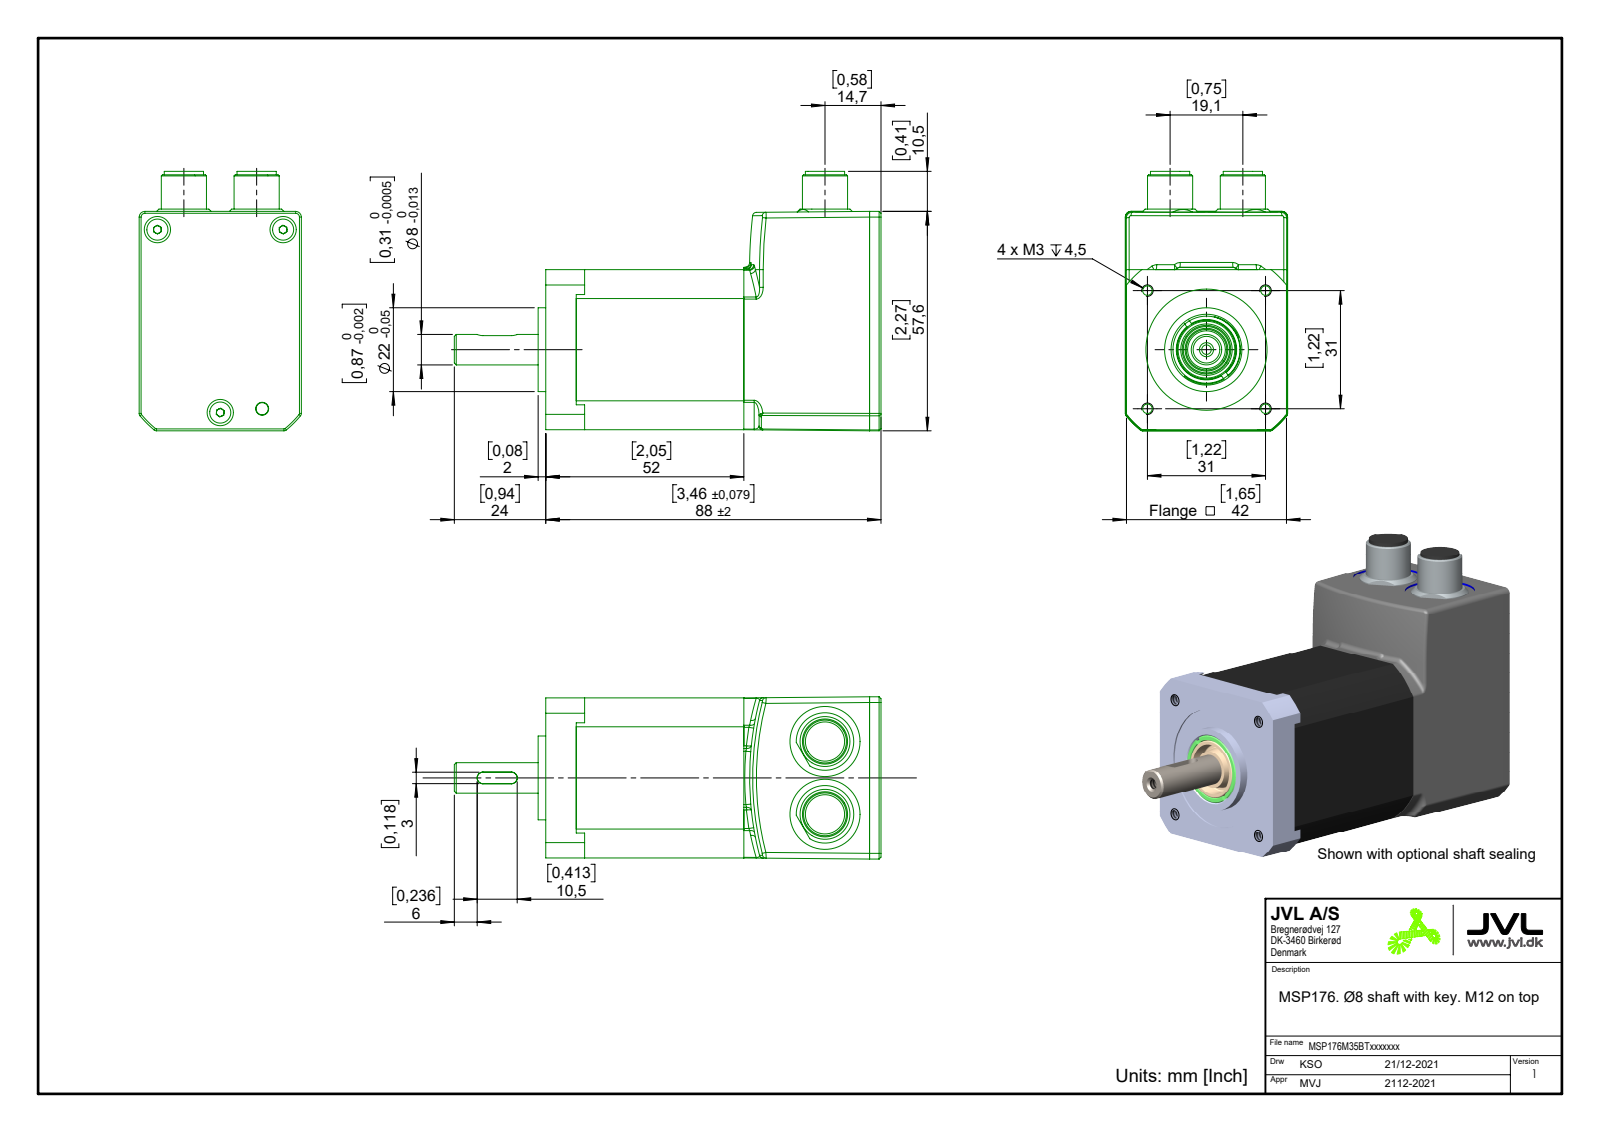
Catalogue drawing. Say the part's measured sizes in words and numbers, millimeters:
The part is named "MSP176M35BTxxxxxxx". Its 3-D file was written by "FreeCAD (AUTOMOTIVE_DESIGN)". It is 5 solids with 335 faces: 136 planar, 73 cylindrical and 126 other. Overall it measures 112 by 68.08 by 42.58 millimeters. Its volume is 175 501 cubic millimeters and its surface area 23 226 square millimeters. Round holes: 5 of diameter 2.5, 3 of diameter 3.3, 2 of diameter 18.4, 1 of diameter 2.8, 1 of diameter 3.4, 1 of diameter 9, 1 of diameter 31.8. Round bosses or shafts: 3 of diameter 5.54, 3 of diameter 3, 2 of diameter 15.1, 2 of diameter 11.85, 2 of diameter 10.3, 1 of diameter 22, 1 of diameter 15.5, 1 of diameter 13.9. Partial cylindrical surfaces (rounded edges, fillets, slot ends): 13 of radius 1, 4 of radius 1.5, 1 of radius 8.8, 1 of radius 24.92, 1 of radius 25.5, 1 of radius 27, 1 of radius 27.29, 1 of radius 80. The main face-to-face distances are 42, 88, 2, 87.5, 0.5, 42.29, 1.5, 86, 2.5, 4. The hole center spacings are 21.92, 31, 35.56, 15.53, 16.03, 35.78, 43.84, 47.01.
